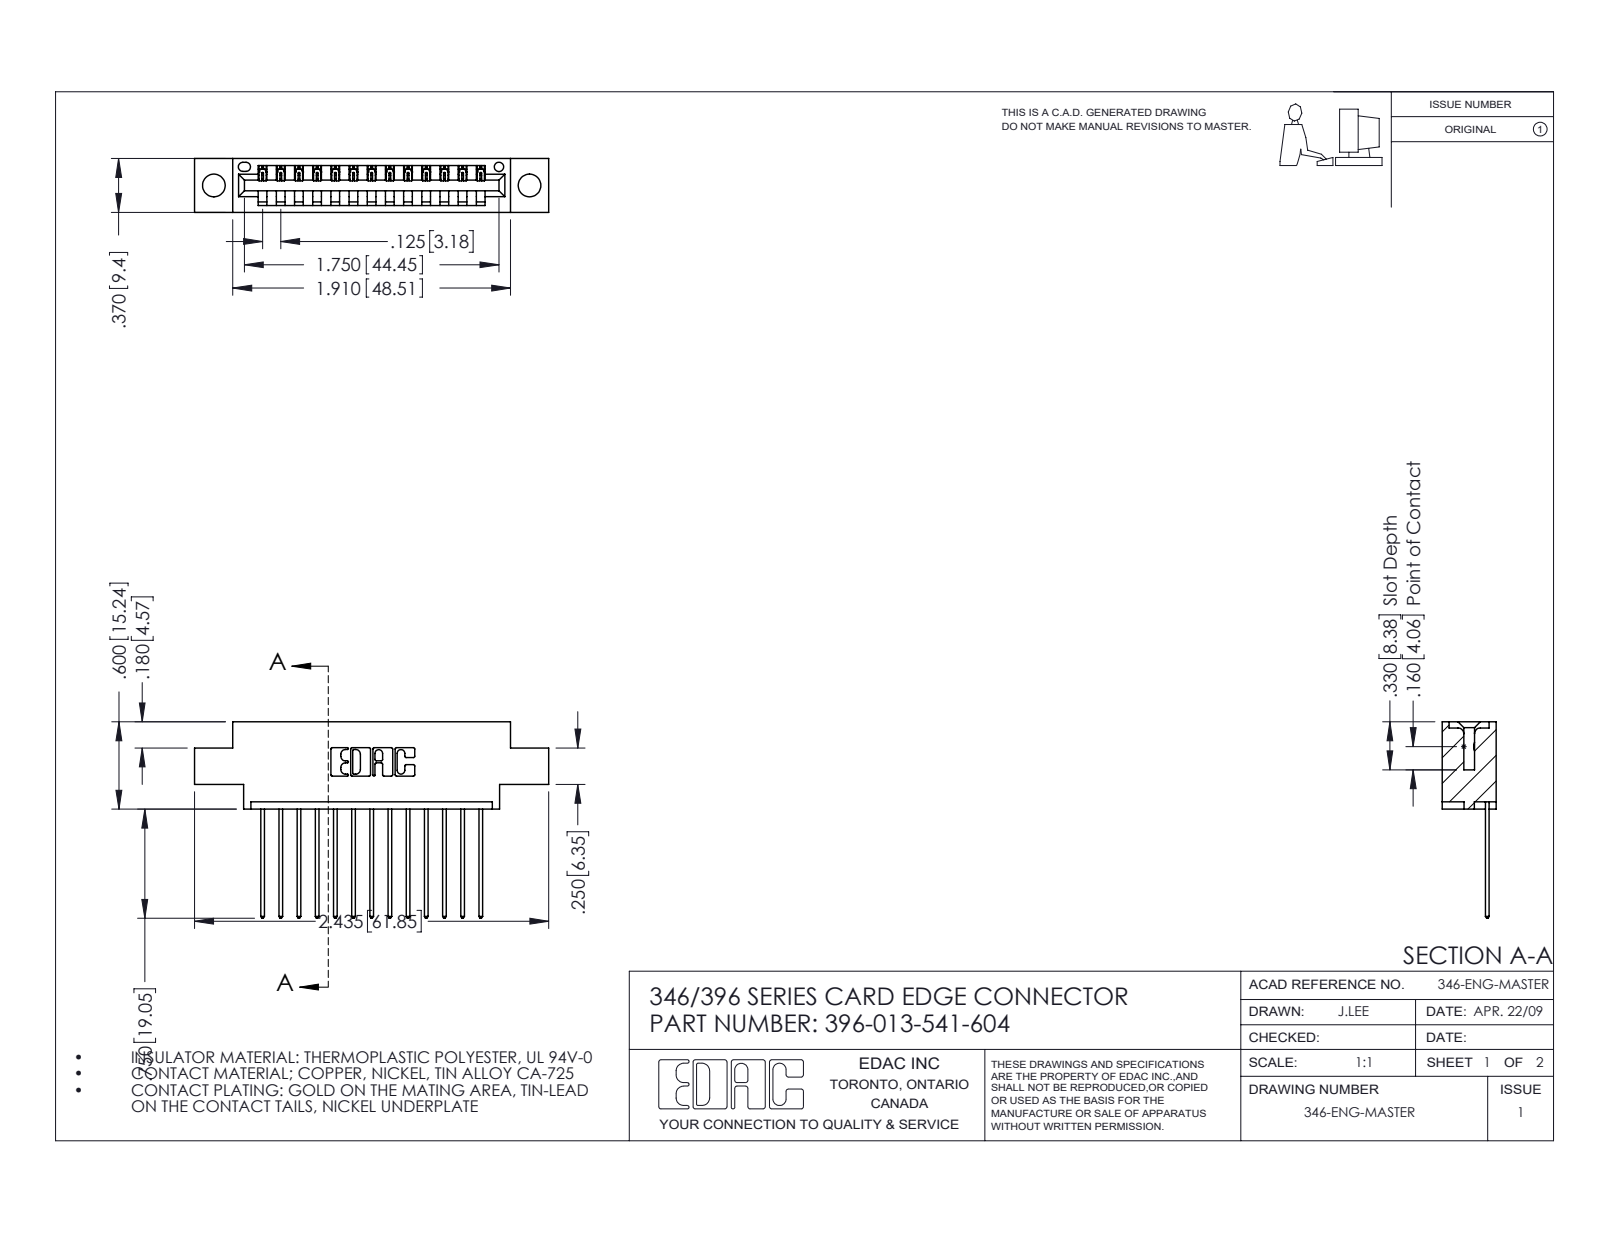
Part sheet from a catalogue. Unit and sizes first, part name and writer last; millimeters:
Units: millimetres
Overall size (bounding box): 61.8 × 34.3 × 9.4
Round holes (diameter × count): ⌀4 ×2, ⌀1.6 ×1
Partial cylindrical surfaces — rounded edges, fillets, slot ends (radius × count): R0.2 ×26, R0.3 ×26, R0.3 ×22, R0.2 ×6, R0.8 ×6, R0.7 ×3, R0.8 ×2, R1 ×2
Main face-to-face distances: 1.2, 8.2, 6.4, 9.4, 1.8, 7.6, 0.6, 3.8, 5.6, 2.5
Hole centre spacings: 6.2, 49.9, 55.1
Volume: 5 520 mm³ · Surface area: 6 806 mm²
Bodies: 14 solids, 880 faces (600 planar, 280 cylindrical, 0 other)
Part name (STEP PRODUCT): 346 Part_0.170 Offset - 0.156 Dia-TH; 345-292-001_345-293-141; 396-013-541-604
STEP written by: SolidWorks 2016 (CONFIG_CONTROL_DESIGN)
